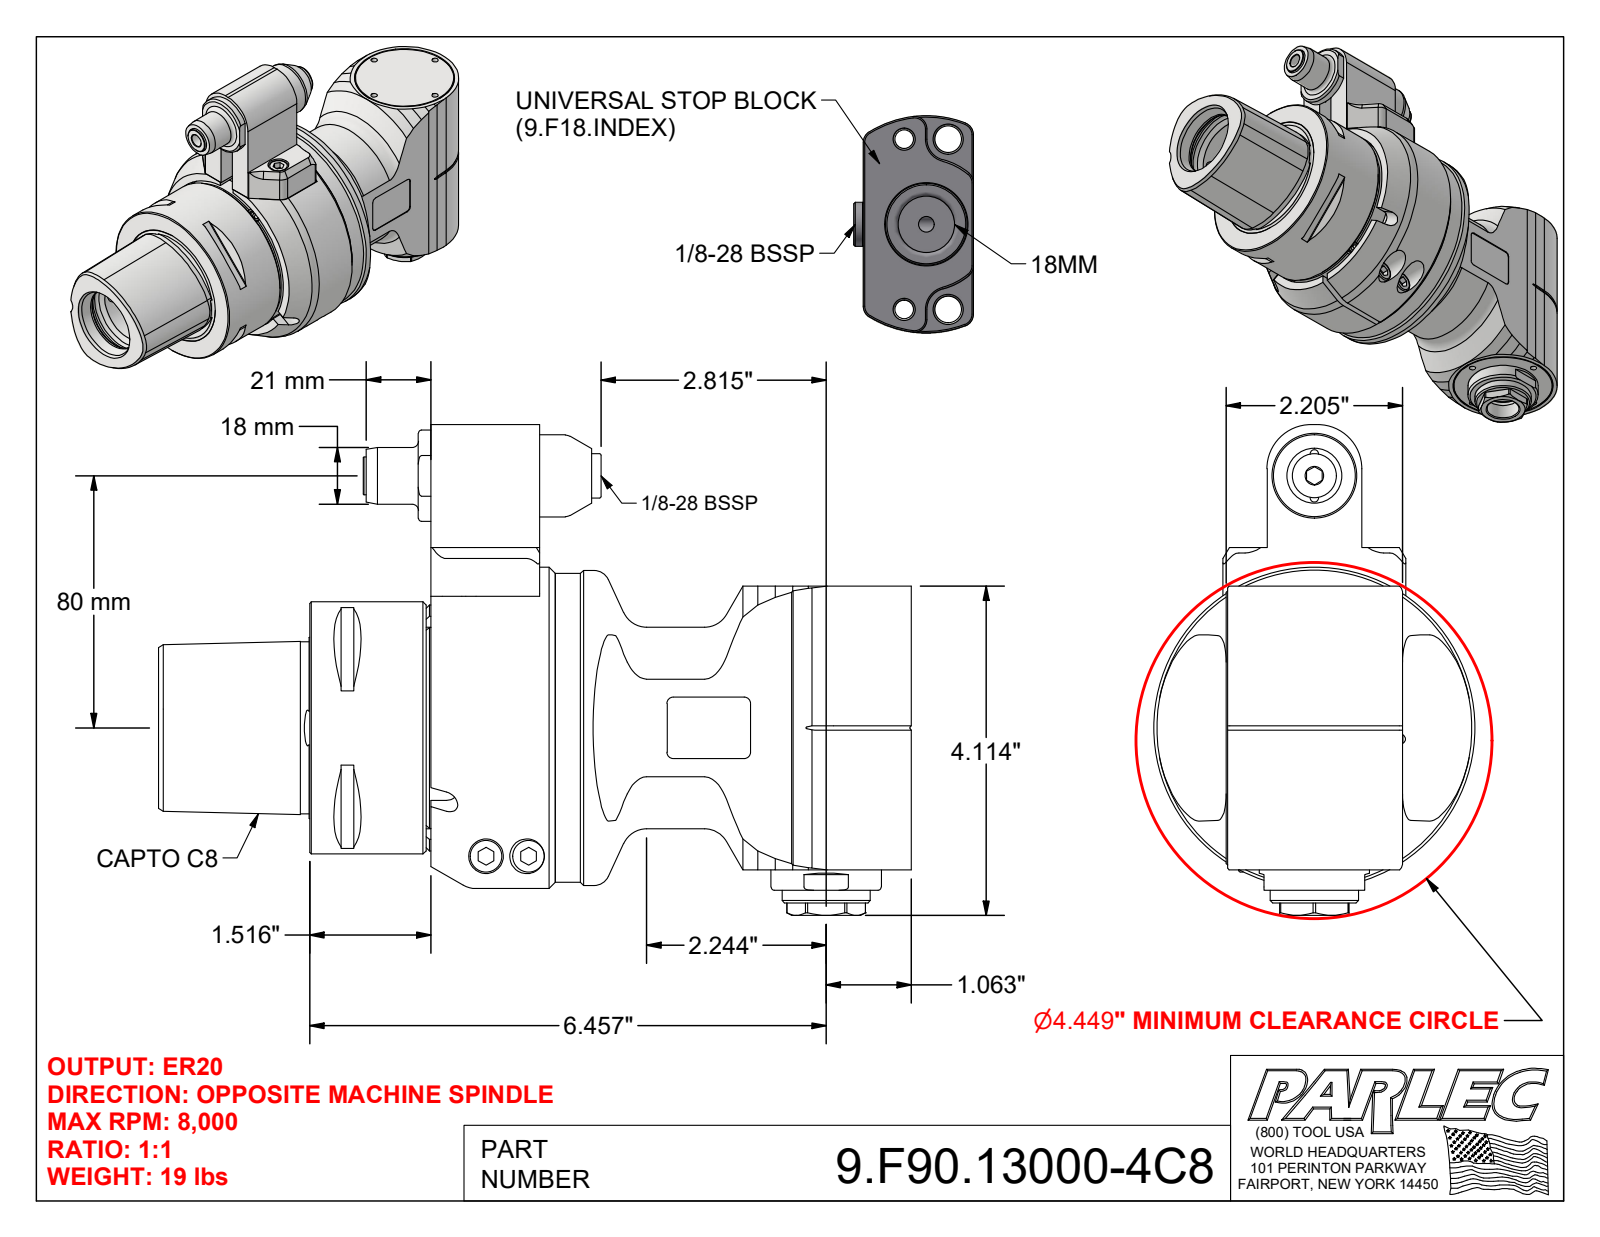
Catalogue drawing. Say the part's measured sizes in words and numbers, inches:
The part is named "9.F90.13000-4C8; 9_F90_13000; 9_GA1_688_2 (EVO, Type1, Capto C8, 80mm)". Its 3-D file was written by "Autodesk Inventor 2022 (AUTOMOTIVE_DESIGN)". It is 5 solids with 519 faces: 236 planar, 124 cylindrical and 159 other. Overall it measures 9.409 by 6.132 by 4.016 inches. Its volume is 68.6 cubic inches and its surface area 230 square inches. Round holes: 4 of diameter 0.126, 2 of diameter 0.102, 2 of diameter 0.197, 2 of diameter 0.409, 2 of diameter 0.433, 2 of diameter 0.492, 1 of diameter 0.098, 1 of diameter 0.118, 1 of diameter 0.157, 1 of diameter 0.256, 1 of diameter 0.276, 1 of diameter 0.335. Round bosses or shafts: 6 of diameter 0.236, 4 of diameter 0.394, 2 of diameter 0.315, 2 of diameter 0.098, 1 of diameter 4.016, 1 of diameter 3.937, 1 of diameter 3.858, 1 of diameter 3.071. Partial cylindrical surfaces (rounded edges, fillets, slot ends): 12 of radius 0.079, 6 of radius 0.118, 5 of radius 0.157, 2 of radius 0.016, 2 of radius 0.02, 2 of radius 0.039, 2 of radius 0.138, 2 of radius 0.197. The main face-to-face distances are 1.26, 0.335, 0.039, 2.205, 1.024, 0.128, 1.811, 3.071, 0.512, 1.516. The hole center spacings are 0.846, 1.197, 0.276, 0.848, 1.693, 0.049, 0.512, 0.551.
